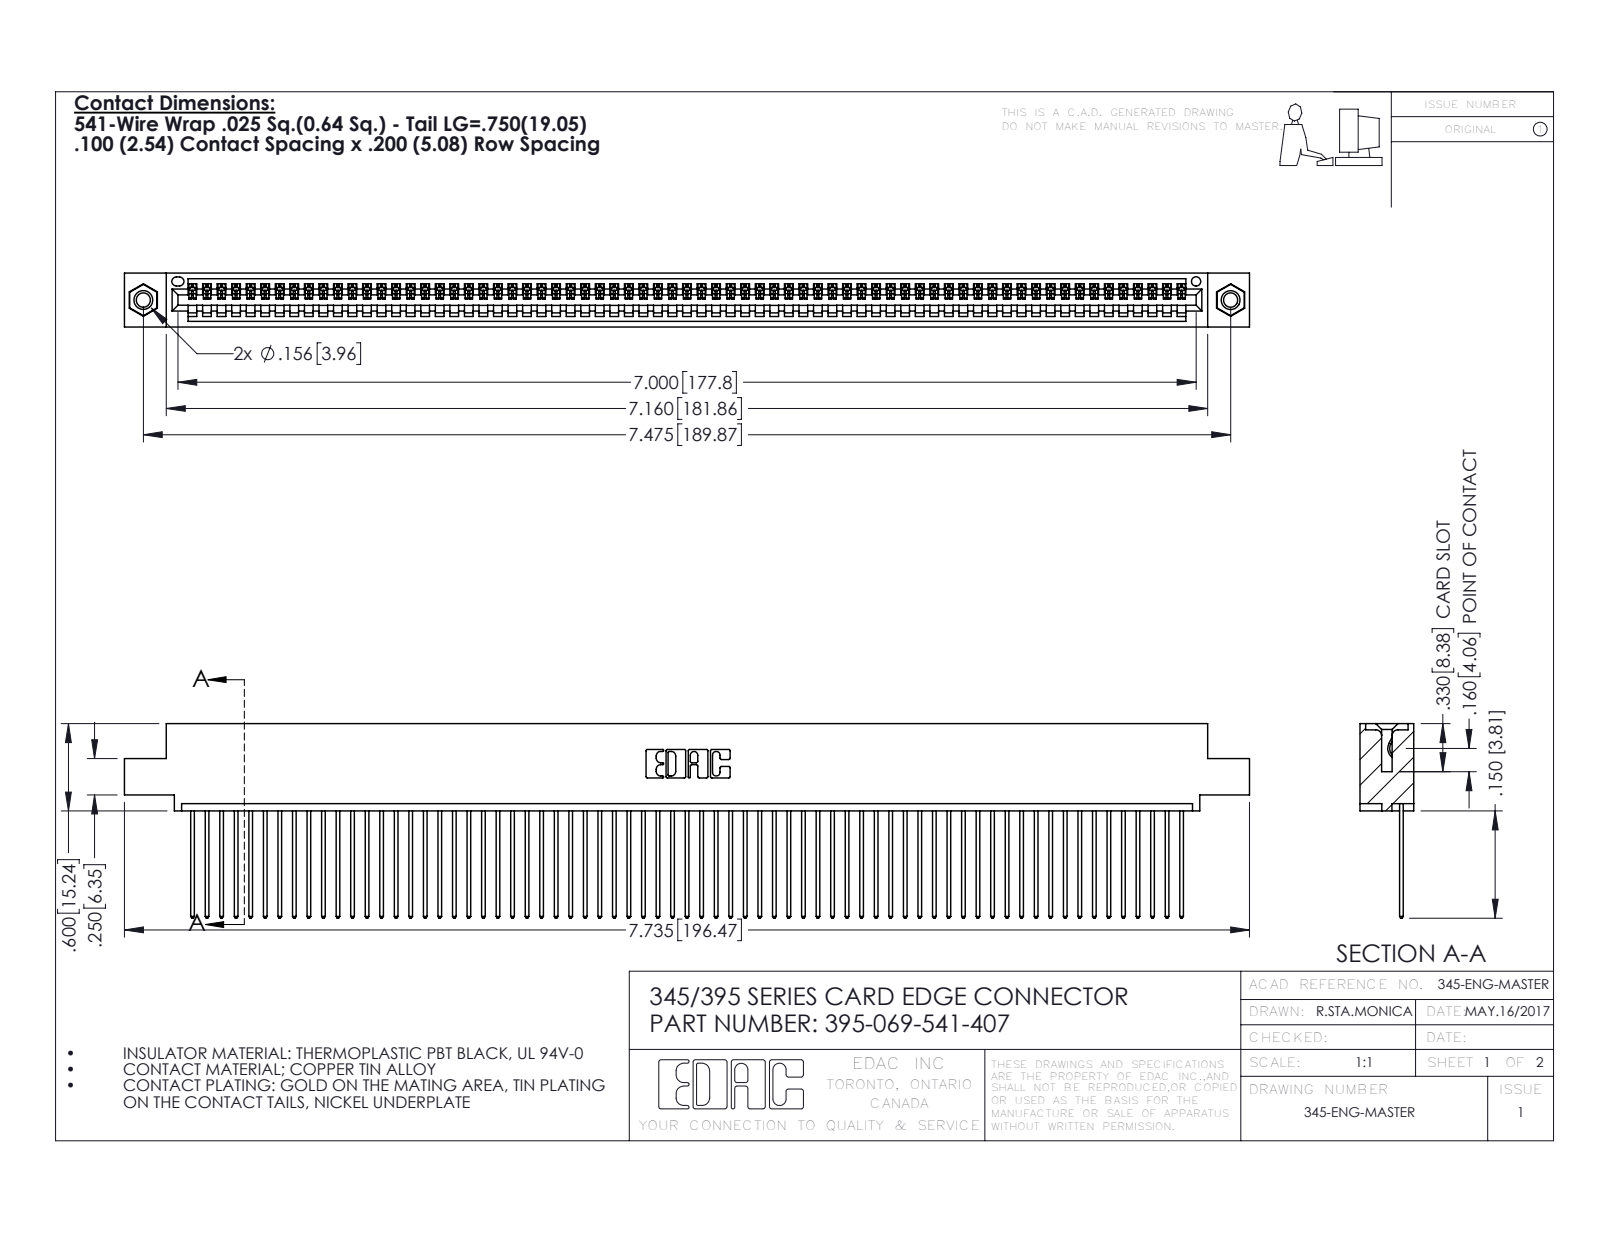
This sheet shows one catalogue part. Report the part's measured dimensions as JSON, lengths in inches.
{"part_name": "395-069-541-407; 345-292-001_345-293-141; 345-250-001_345-250-005-103; 345 Part_0.110 Offset - 0.156 Dia-TI", "step_written_by": "SolidWorks 2016 (CONFIG_CONTROL_DESIGN)", "units": "inches", "bodies": {"solids": 72, "faces": 4192, "planar": 2876, "cylindrical": 1300, "other": 16}, "overall_size": [7.735, 1.337, 0.37], "volume_in3": 1.161, "surface_area_in2": 42.01, "round_holes": [[0.098, 2], [0.125, 2], [0.156, 2], [0.064, 1]], "round_bosses_or_shafts": [[0.155, 2]], "partial_cylinders_radius": [[0.006, 138], [0.01, 138], [0.01, 22], [0.007, 6], [0.031, 6], [0.026, 3], [0.031, 2], [0.04, 2]], "face_to_face_distances": [0.072, 0.298, 0.098, 0.272, 0.025, 0.37, 0.2, 0.225, 0.149, 0.072], "hole_center_spacings": [0.27, 7.239, 7.475]}
